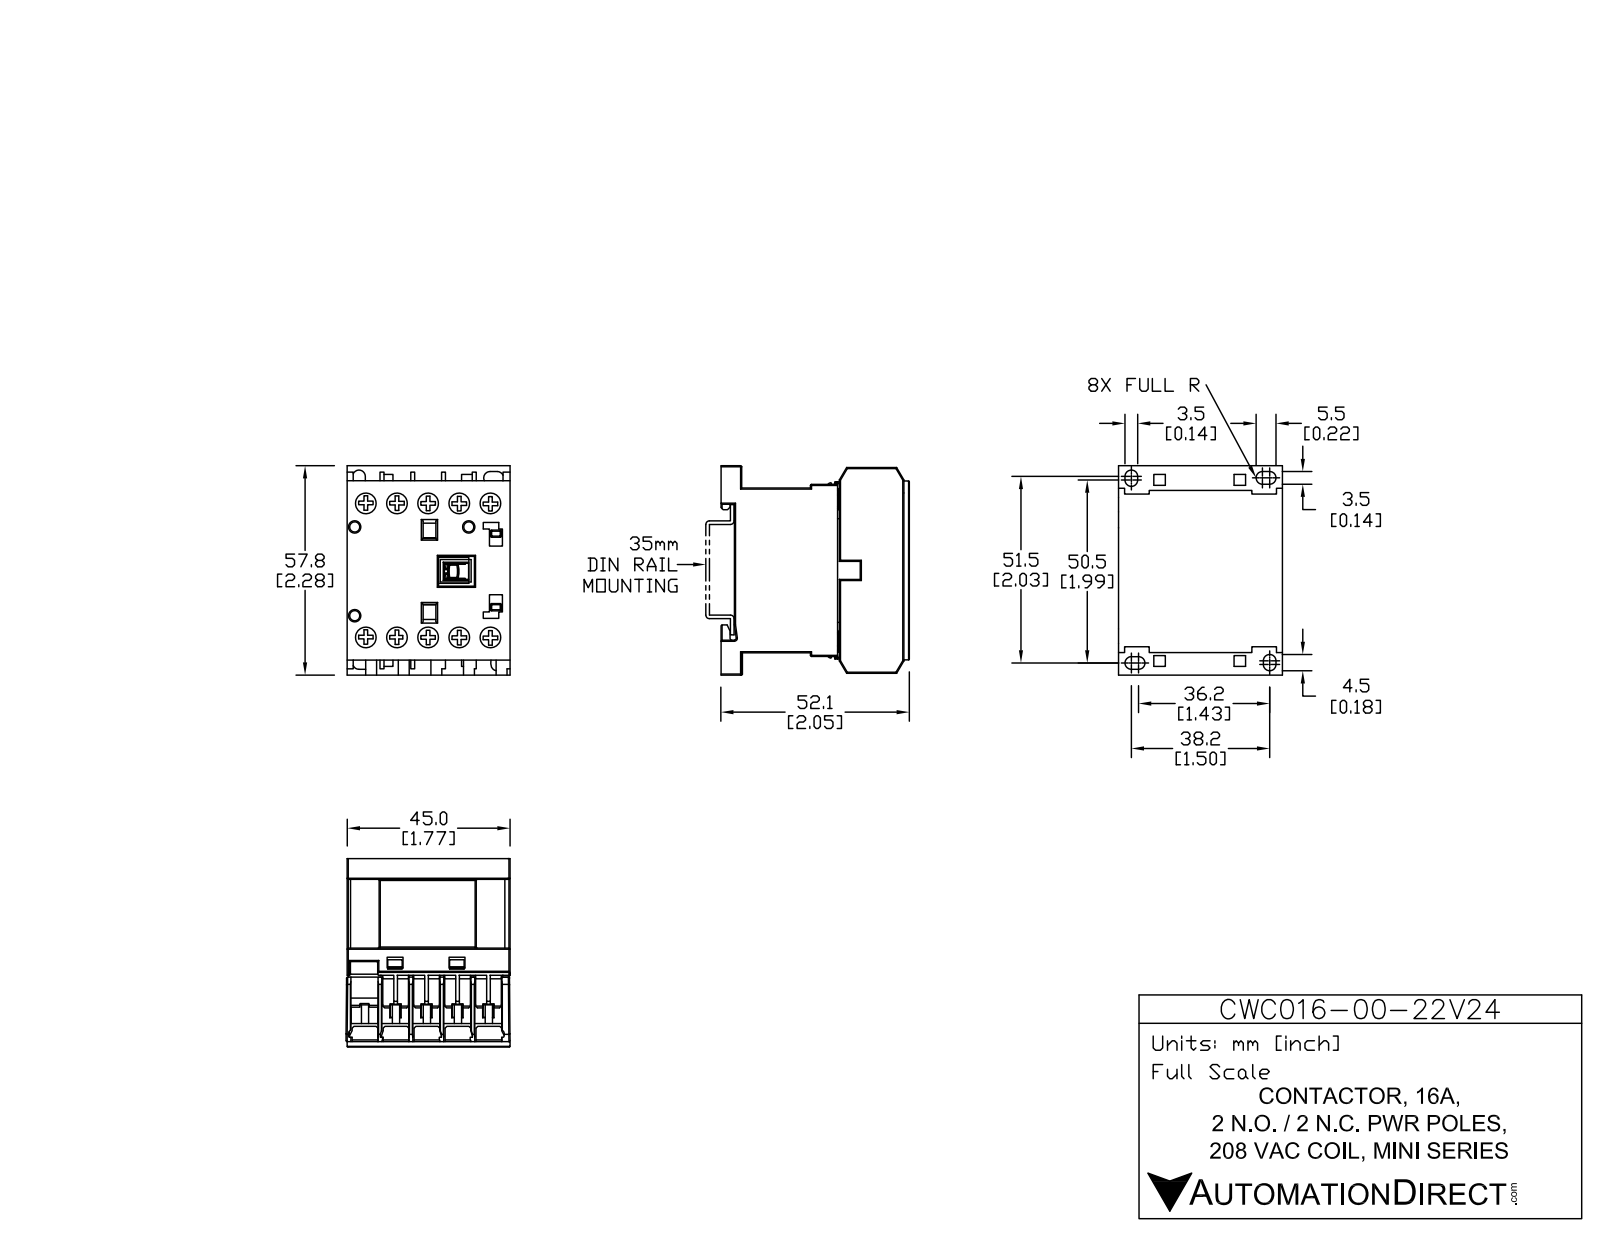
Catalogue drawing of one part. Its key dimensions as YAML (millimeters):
part_name: "CWC16-00-22V24"
step_written_by: "SolidWorks 2013 (AUTOMOTIVE_DESIGN)"
units: millimeters
bodies: {solids: 15, faces: 535, planar: 445, cylindrical: 90, other: 0}
overall_size: [58.04, 52.12, 45.75]
volume: 97133
surface_area: 30437
round_holes:
  - {diameter: 6.2, count: 10}
  - {diameter: 2.8, count: 3}
round_bosses_or_shafts:
  - {diameter: 5.9, count: 10}
partial_cylinders:
  - {radius: 0.3, count: 20}
  - {radius: 1.72, count: 6}
  - {radius: 1.73, count: 2}
  - {radius: 0.32, count: 1}
  - {radius: 0.42, count: 1}
  - {radius: 0.55, count: 1}
face_to_face_distances: [8.25, 45.5, 1.25, 16.5, 9.5, 5.5, 17.75, 5.13, 10.63, 7]
hole_center_spacings: [8.55, 37.94, 17.1, 40.72, 36.96, 25.65, 44.99, 6.91]
